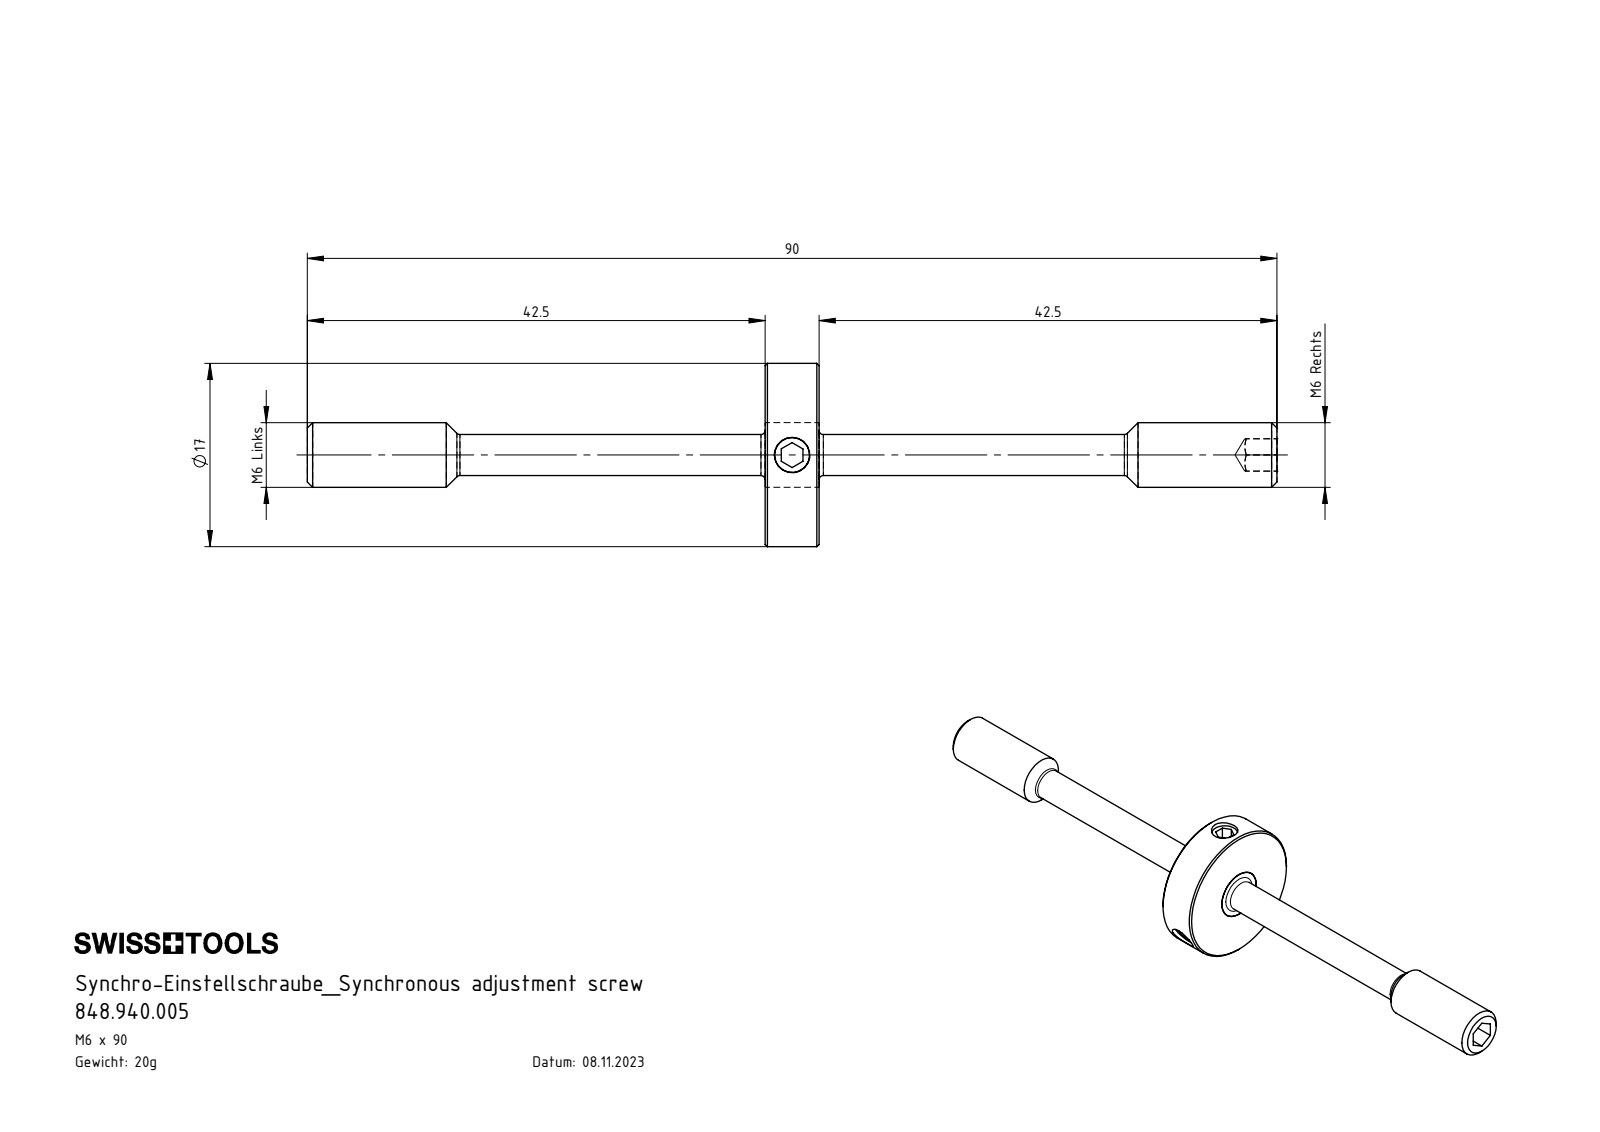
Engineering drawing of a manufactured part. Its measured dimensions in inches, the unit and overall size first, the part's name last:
Units: inches
Overall size (bounding box): 3.543 × 0.669 × 0.669
Round holes (diameter × count): ⌀0.13 ×3
Round bosses / shafts (diameter × count): ⌀0.157 ×3, ⌀0.669 ×1, ⌀0.236 ×1, ⌀0.15 ×1
Main face-to-face distances: 0.197, 1.673, 1.87, 0.079, 0.098, 0.118, 3.543, 1.732, 1.811, 0.059
Volume: 0.154 in³ · Surface area: 3.993 in²
Bodies: 5 solids, 99 faces (39 planar, 26 cylindrical, 34 other)
Part name (STEP PRODUCT): Z94-ER3.001.090_A; Z42-ER3.002.005_A; ISO 4026 - M4 x 5; 848.940.005
STEP written by: SolidWorks 2022 (AUTOMOTIVE_DESIGN)
